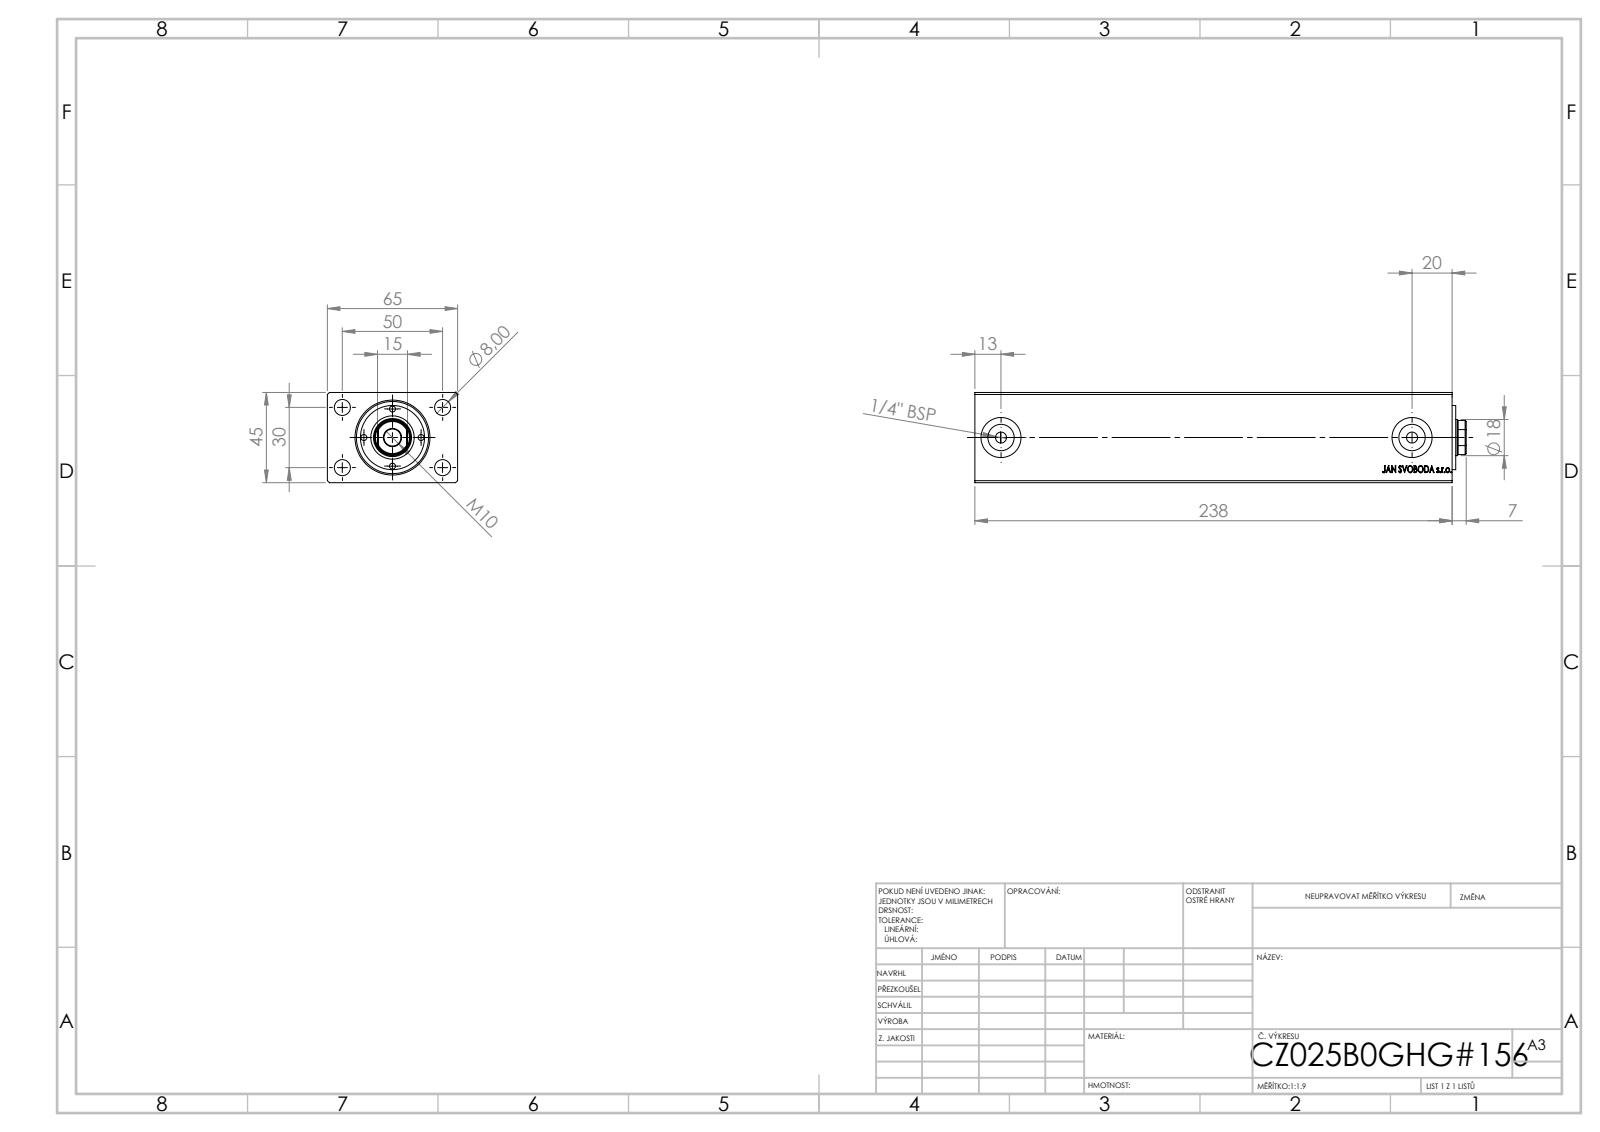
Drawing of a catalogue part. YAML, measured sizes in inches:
part_name: "V500CZ_B_VC; V500CZ"
step_written_by: "SolidWorks 2019 (CONFIG_CONTROL_DESIGN)"
units: inches
bodies: {solids: 3, faces: 873, planar: 399, cylindrical: 58, other: 416}
overall_size: [9.646, 2.559, 1.772]
volume: 39.33
surface_area: 155.8
round_holes:
  - {diameter: 0.118, count: 4}
  - {diameter: 0.315, count: 4}
  - {diameter: 0.217, count: 2}
  - {diameter: 0.518, count: 2}
  - {diameter: 0.787, count: 2}
  - {diameter: 0.335, count: 1}
  - {diameter: 0.709, count: 1}
  - {diameter: 0.748, count: 1}
  - {diameter: 0.984, count: 1}
  - {diameter: 1.417, count: 1}
round_bosses_or_shafts:
  - {diameter: 1.26, count: 1}
partial_cylinders:
  - {radius: 0.335, count: 1}
face_to_face_distances: [1.772, 2.559, 9.37, 0.276, 9.362, 8.866, 0.496, 0.504, 0.071, 0.205]
hole_center_spacings: [0.561, 0.726, 0.793, 0.985, 1.148, 1.515, 1.654, 1.122]
